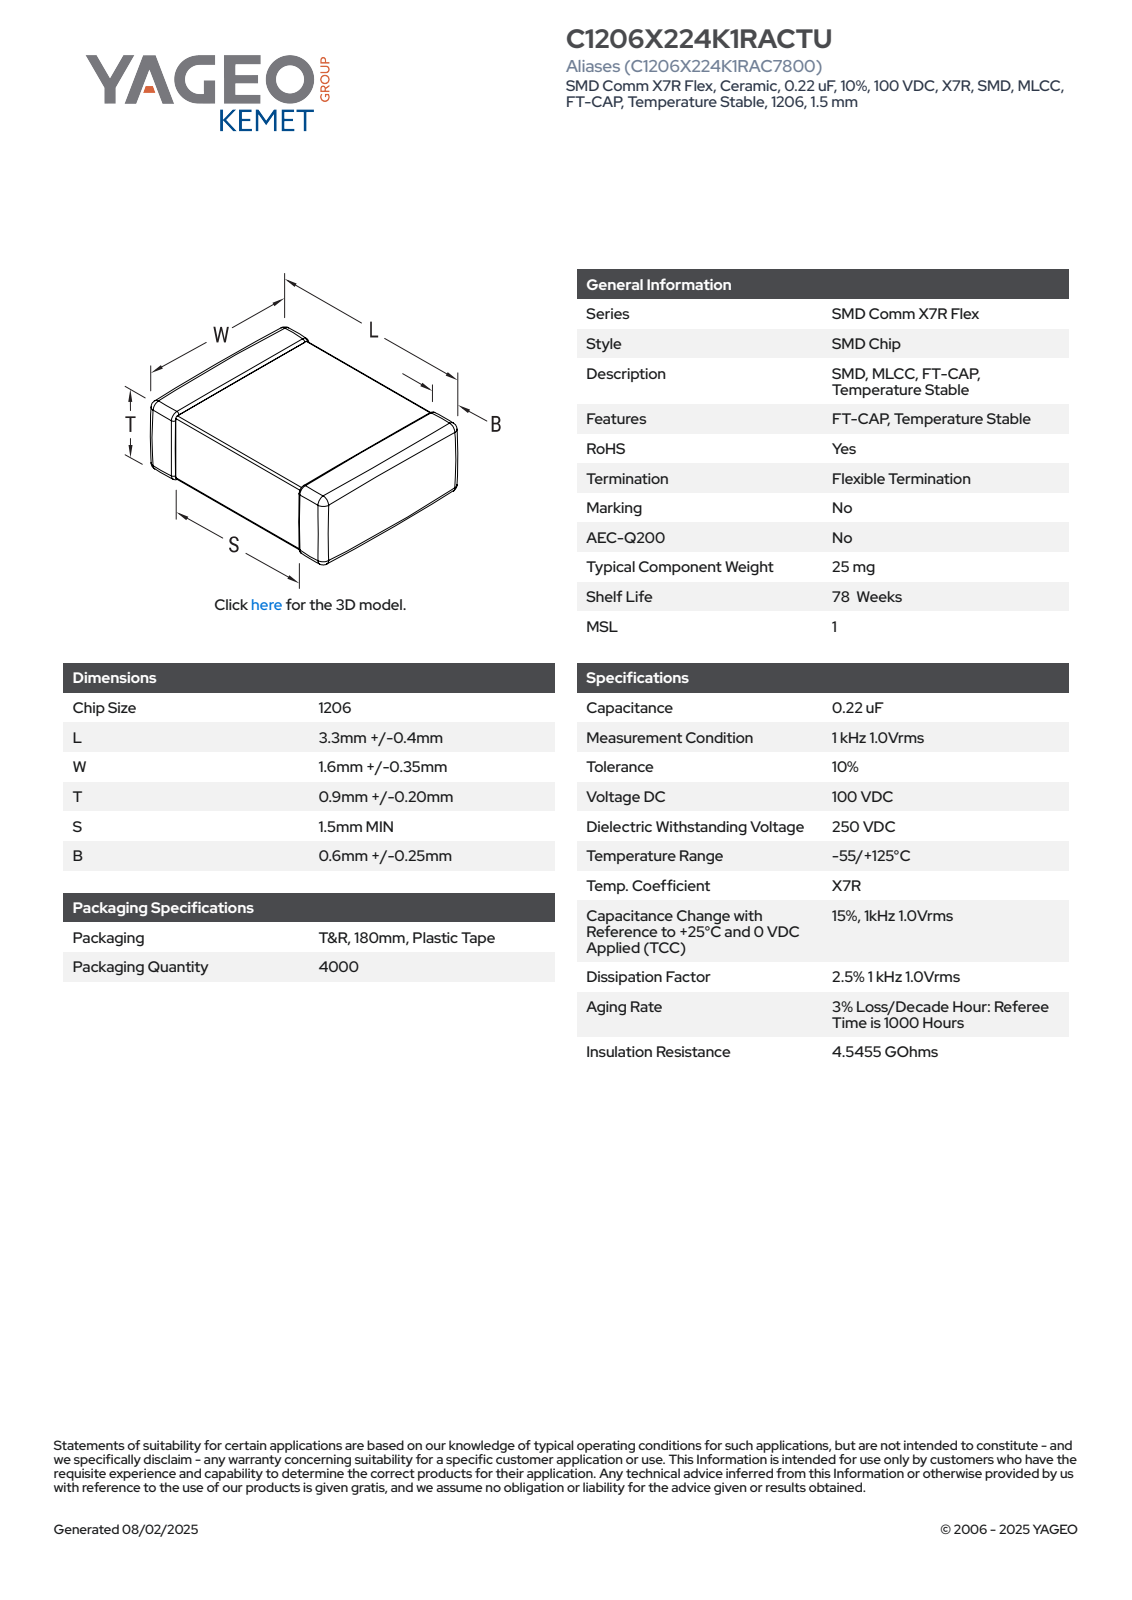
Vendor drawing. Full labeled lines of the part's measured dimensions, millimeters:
Part name (STEP PRODUCT): CCS_CCSTDNOS_1206_L3.7W1.95T1.1B0.85
STEP written by: SolidWorks 2014 (AUTOMOTIVE_DESIGN)
Units: millimetres
Bodies: 4 solids, 125 faces (71 planar, 38 cylindrical, 16 other)
Overall size (bounding box): 3.7 × 1.95 × 1.1
Volume: 7 mm³ · Surface area: 26 mm²
Main face-to-face distances: 1.06, 1.02, 1.91, 1.1, 3.7, 1.87, 1.95, 0.86, 0.82, 1.05
